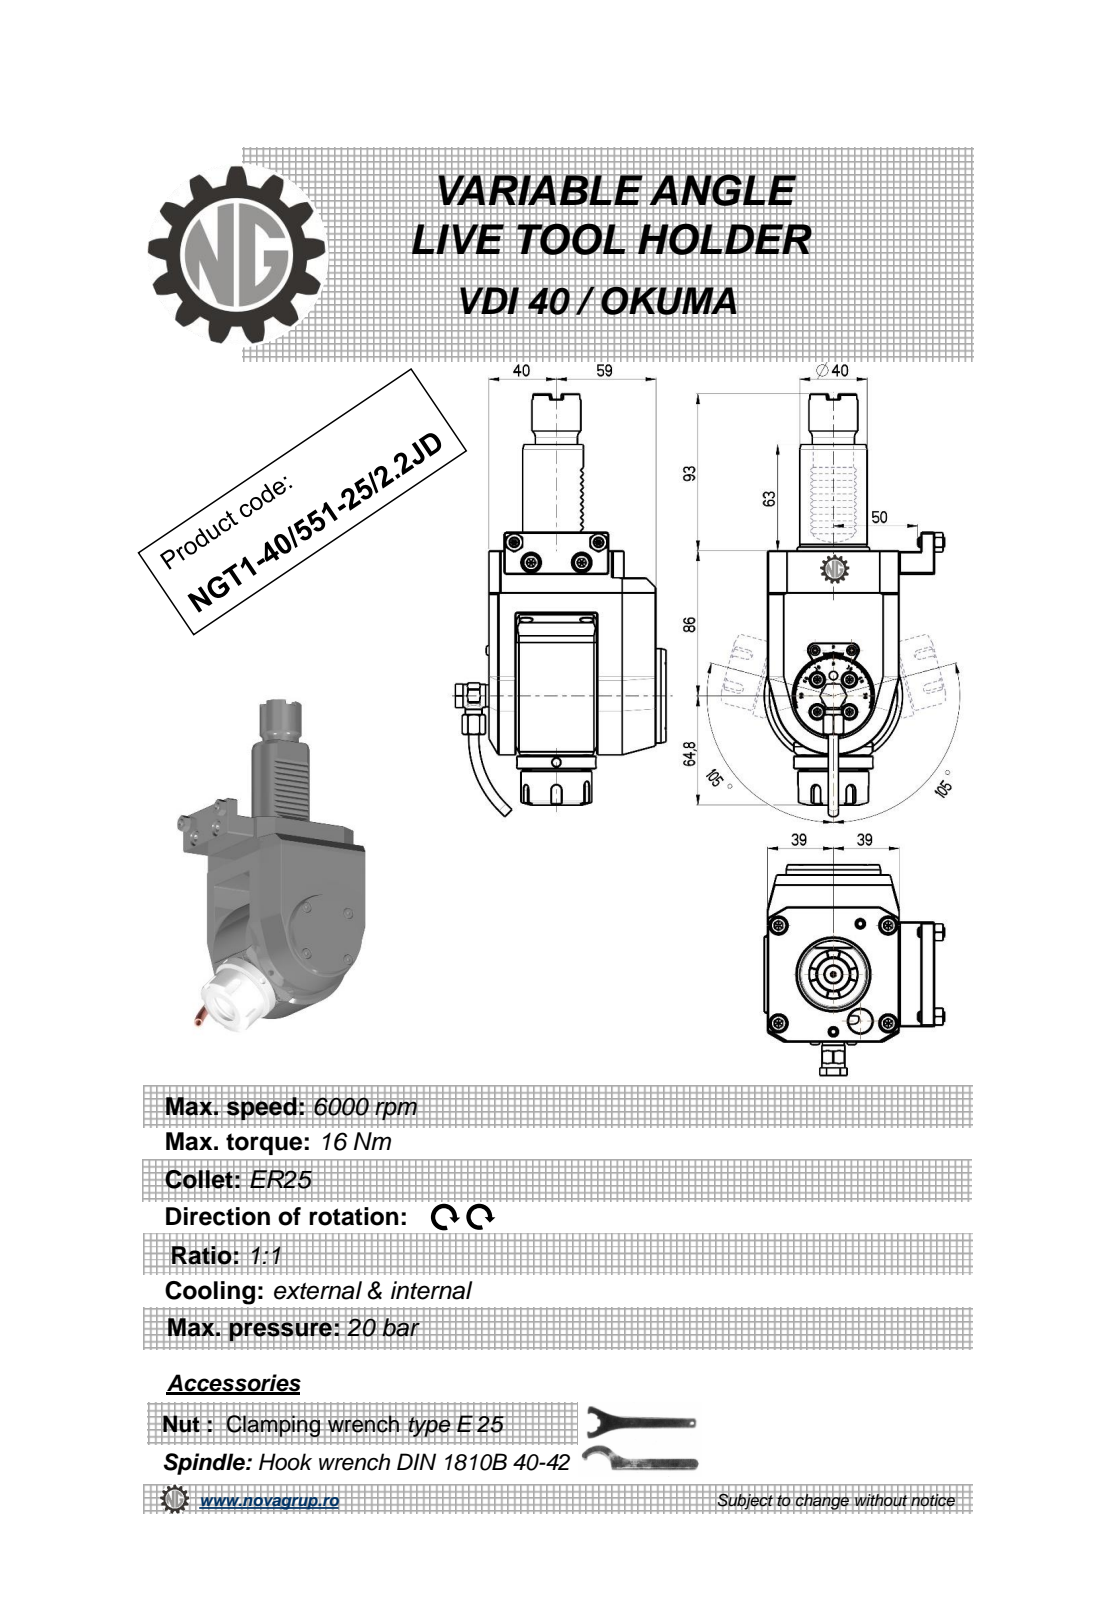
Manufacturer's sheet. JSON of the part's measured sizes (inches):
{"part_name": "NGT1_40_551_25_2_2JD", "step_written_by": "PRO/ENGINEER BY PARAMETRIC TECHNOLOGY CORPORATION, 2010280 (CONFIG_CONTROL_DESIGN)", "units": "inches", "bodies": {"solids": 1, "faces": 604, "planar": 243, "cylindrical": 128, "other": 233}, "overall_size": [9.869, 4.917, 4.213], "volume_in3": 59.04, "surface_area_in2": 136.9, "round_holes": [[0.157, 3], [0.197, 2], [0.118, 1], [0.244, 1], [0.354, 1], [0.394, 1], [0.433, 1], [0.799, 1]], "round_bosses_or_shafts": [[0.236, 4], [0.224, 2], [2.205, 1], [1.85, 1], [1.654, 1], [1.575, 1], [1.378, 1], [1.142, 1]], "partial_cylinders_radius": [[0.012, 10], [0.012, 10], [0.118, 5], [0.02, 4], [0.394, 3], [0.039, 2], [0.303, 1], [1.378, 1]], "face_to_face_distances": [3.898, 1.457, 0.63, 3.071, 0.827, 2.52, 0.236, 4.134, 1.89, 0.315], "hole_center_spacings": [0.016, 1.553, 1.929, 1.945]}
